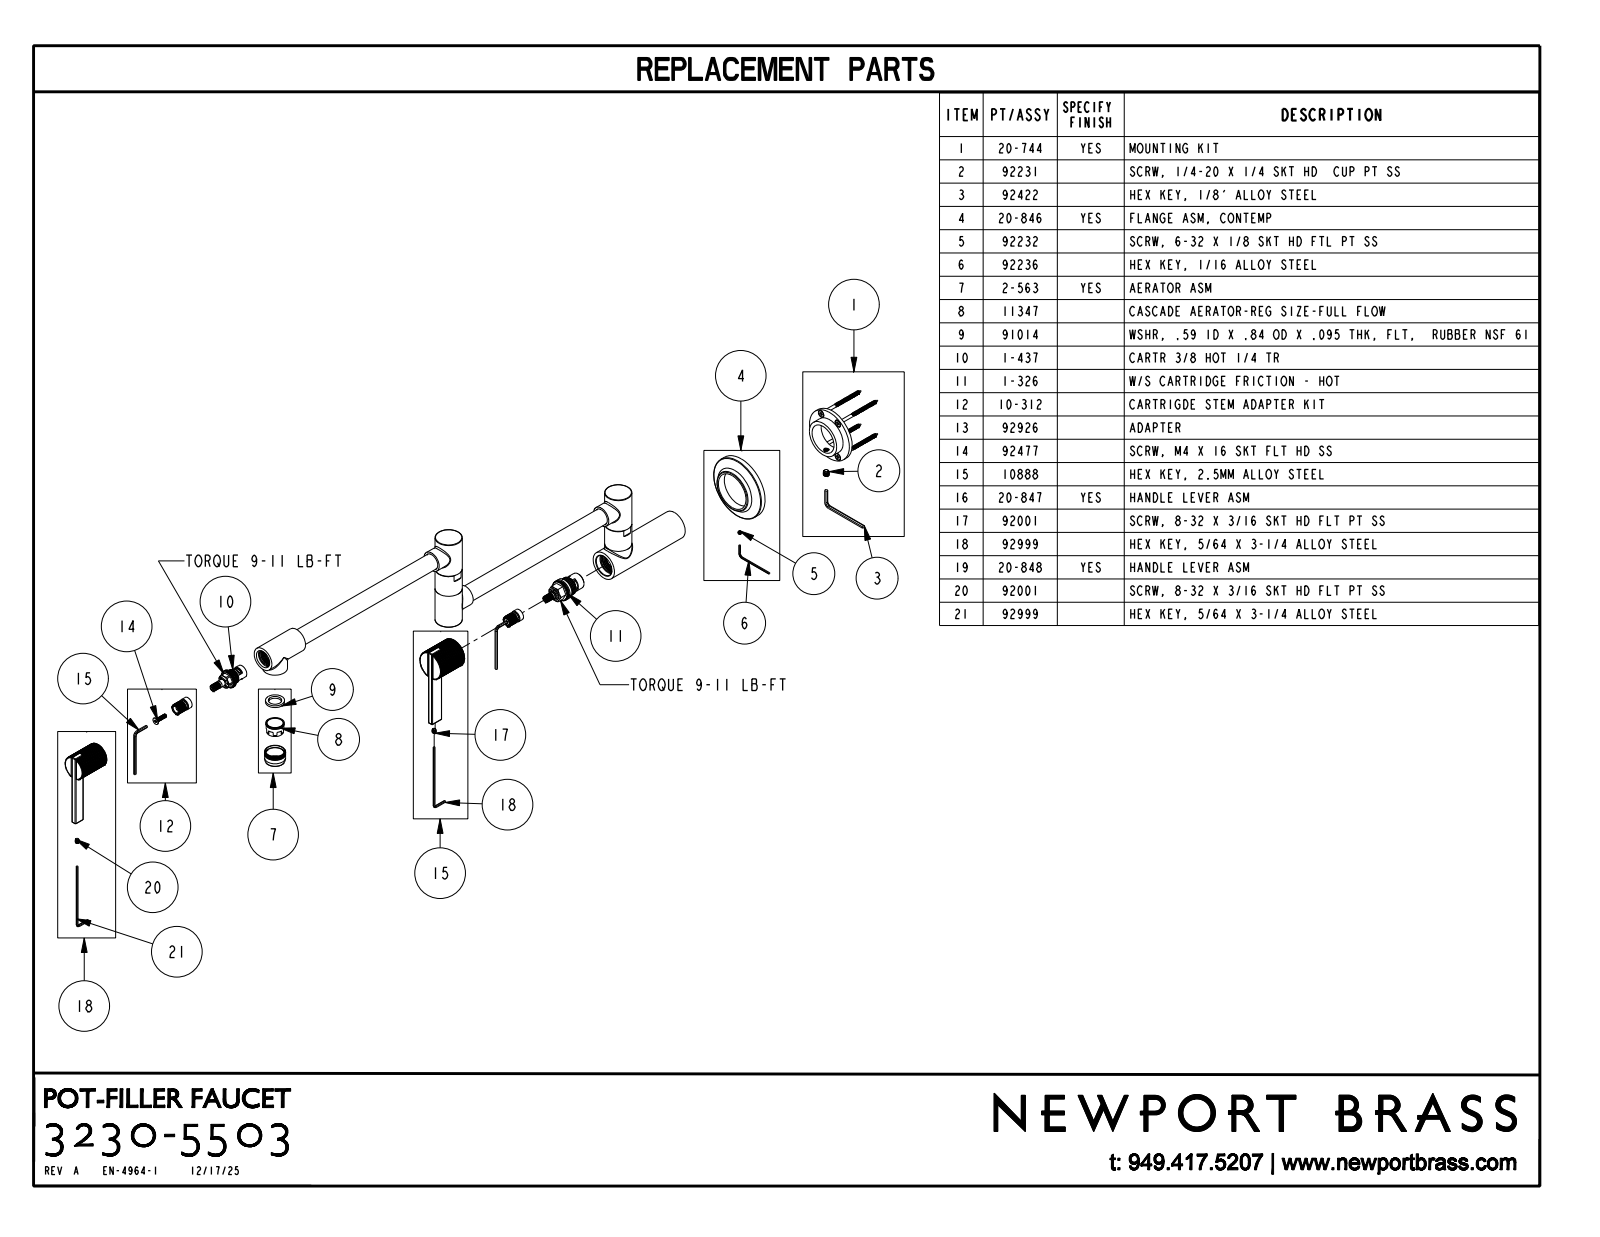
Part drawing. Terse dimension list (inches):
name: 3230-5503
written by: CREO PARAMETRIC BY PTC INC, 2023134 (CONFIG_CONTROL_DESIGN)
unit: in
bodies: 5 solids, 702 faces (394 planar, 246 cylindrical, 62 other)
size: 27.2 × 9.496 × 2.958
volume: 31.38 in³; area: 157.2 in²
holes: 2× ⌀0.76, 2× ⌀0.95, 1× ⌀0.665, 1× ⌀0.792, 1× ⌀0.975
bosses: 2× ⌀1.2, 2× ⌀1.1, 2× ⌀0.94, 2× ⌀0.75, 1× ⌀2.958, 1× ⌀1.325, 1× ⌀0.925, 1× ⌀0.786
rounds: 28× R0.03, 4× R0.06, 1× R0.115, 1× R0.281
face distances: 2.86, 0.235, 0.015, 0.25, 1.676, 0.02, 0.07, 1.746, 0.57, 4.428
hole spacings: 2.72, 2.86, 5.58, 10.57, 10.82, 21.39
